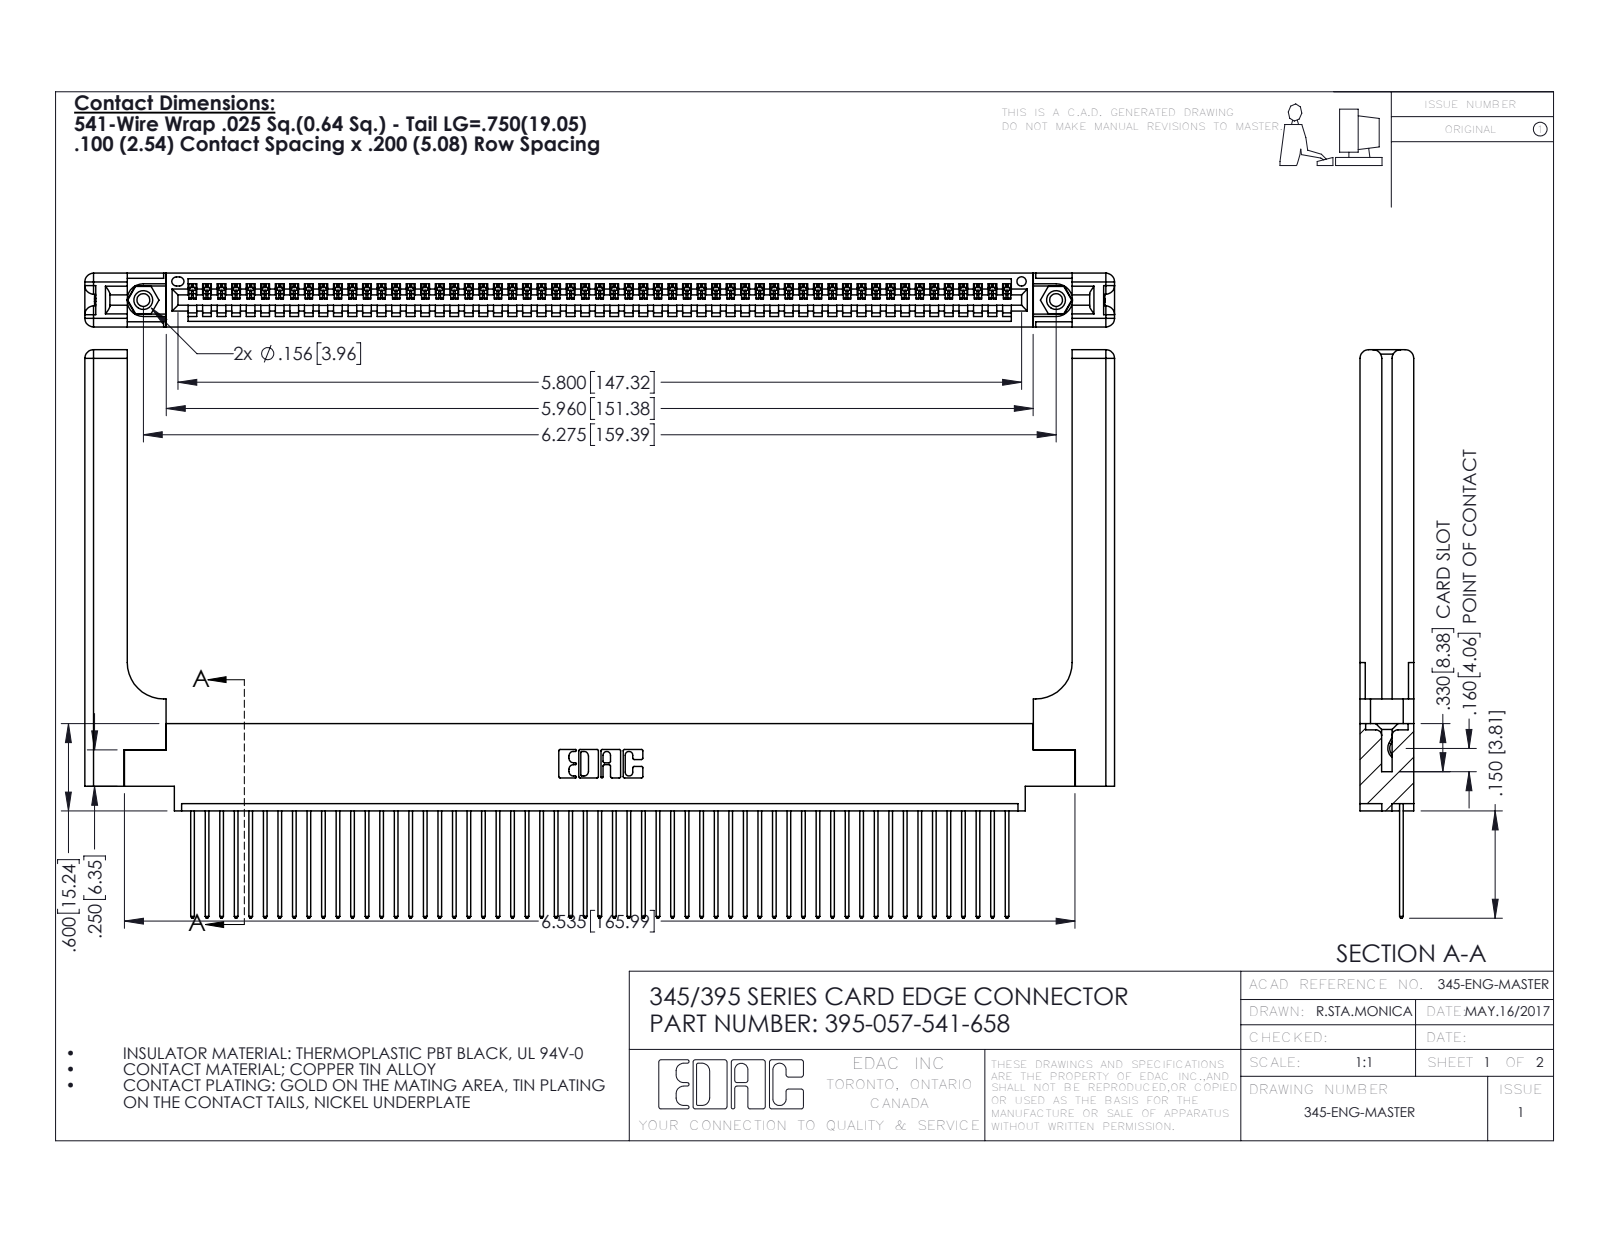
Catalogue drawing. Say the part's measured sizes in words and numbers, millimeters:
The part is named "345-292-001_345-293-141; 395-057-541-658; 345-250-001_345-250-001-102; 345-220-058_345-220-058 (+1 more)". Its 3-D file was written by "SolidWorks 2016 (CONFIG_CONTROL_DESIGN)". It is 62 solids with 3692 faces: 2512 planar, 1120 cylindrical and 60 other. Overall it measures 179.8 by 99.2 by 9.4 millimeters. Its volume is 25 780 cubic millimeters and its surface area 29 700 square millimeters. Round holes: 2 of diameter 2.3, 2 of diameter 3.2, 2 of diameter 4, 1 of diameter 1.6. Round bosses or shafts: 2 of diameter 3.9. Partial cylindrical surfaces (rounded edges, fillets, slot ends): 114 of radius 0.2, 114 of radius 0.3, 22 of radius 0.3, 16 of radius 1.5, 6 of radius 0.2, 6 of radius 0.8, 3 of radius 0.7, 2 of radius 0.8. The main face-to-face distances are 1.8, 7.6, 9.4, 2.5, 6.9, 0.6, 5.1, 5.7, 3.8, 3.8. The hole center spacings are 6.9, 153.4, 159.4.
